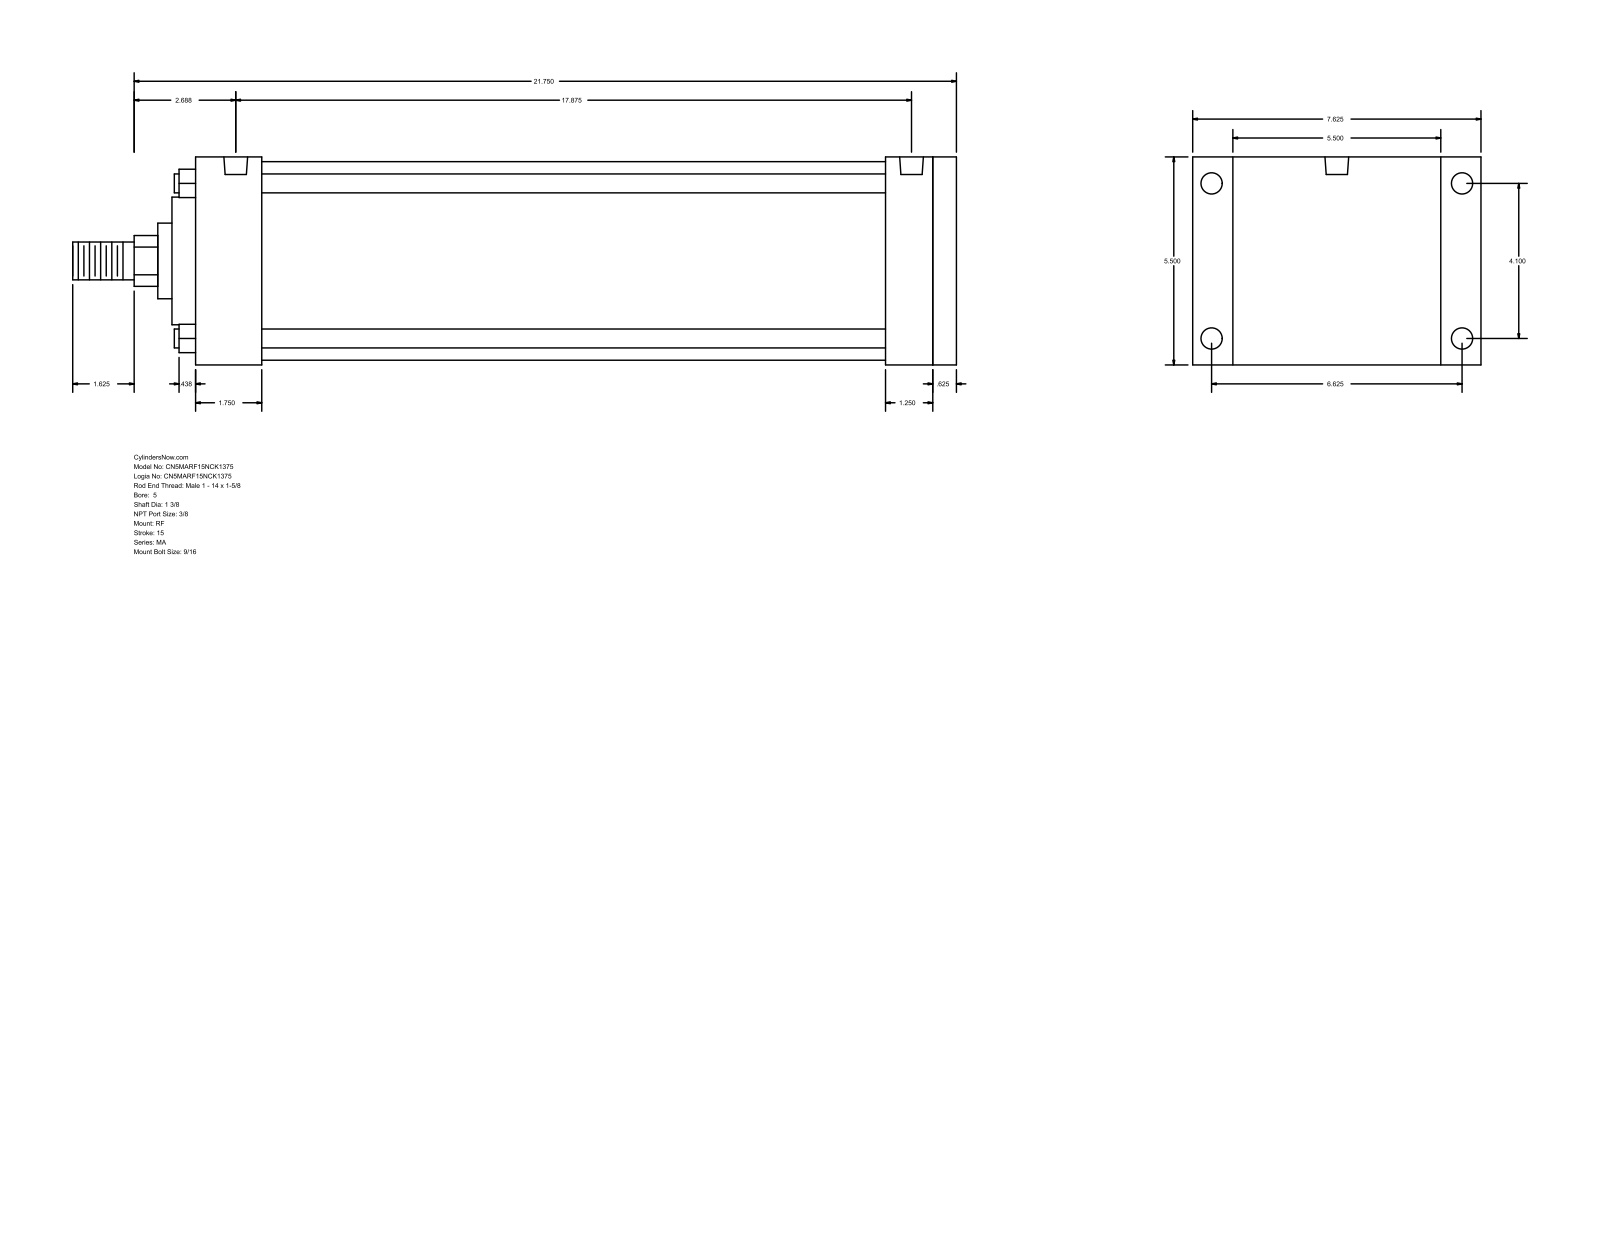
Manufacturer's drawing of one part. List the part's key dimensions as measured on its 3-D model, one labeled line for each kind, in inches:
Part name (STEP PRODUCT): MA_RF__0500_1.375
STEP written by: GSSL Pune (CONFIG_CONTROL_DESIGN)
Units: inches
Bodies: 0 solids, 94 faces (65 planar, 29 cylindrical, 0 other)
Overall size (bounding box): 23.375 × 7.625 × 5.5
Round holes (diameter × count): ⌀0.437 ×4, ⌀0.563 ×4, ⌀0.627 ×2
Round bosses / shafts (diameter × count): ⌀0.5 ×4, ⌀5.25 ×1, ⌀3.375 ×1, ⌀2 ×1, ⌀1.375 ×1, ⌀1 ×1
Partial cylindrical surfaces — rounded edges, fillets, slot ends (radius × count): R0.672 ×1
Main face-to-face distances: 5.5, 20.125, 0.625, 19.5, 1.75, 17.75, 18.375, 18.25, 16.5, 1.25
Hole centre spacings: 0.188, 4.1, 6.625, 7.791, 17.5, 17.687, 17.875
